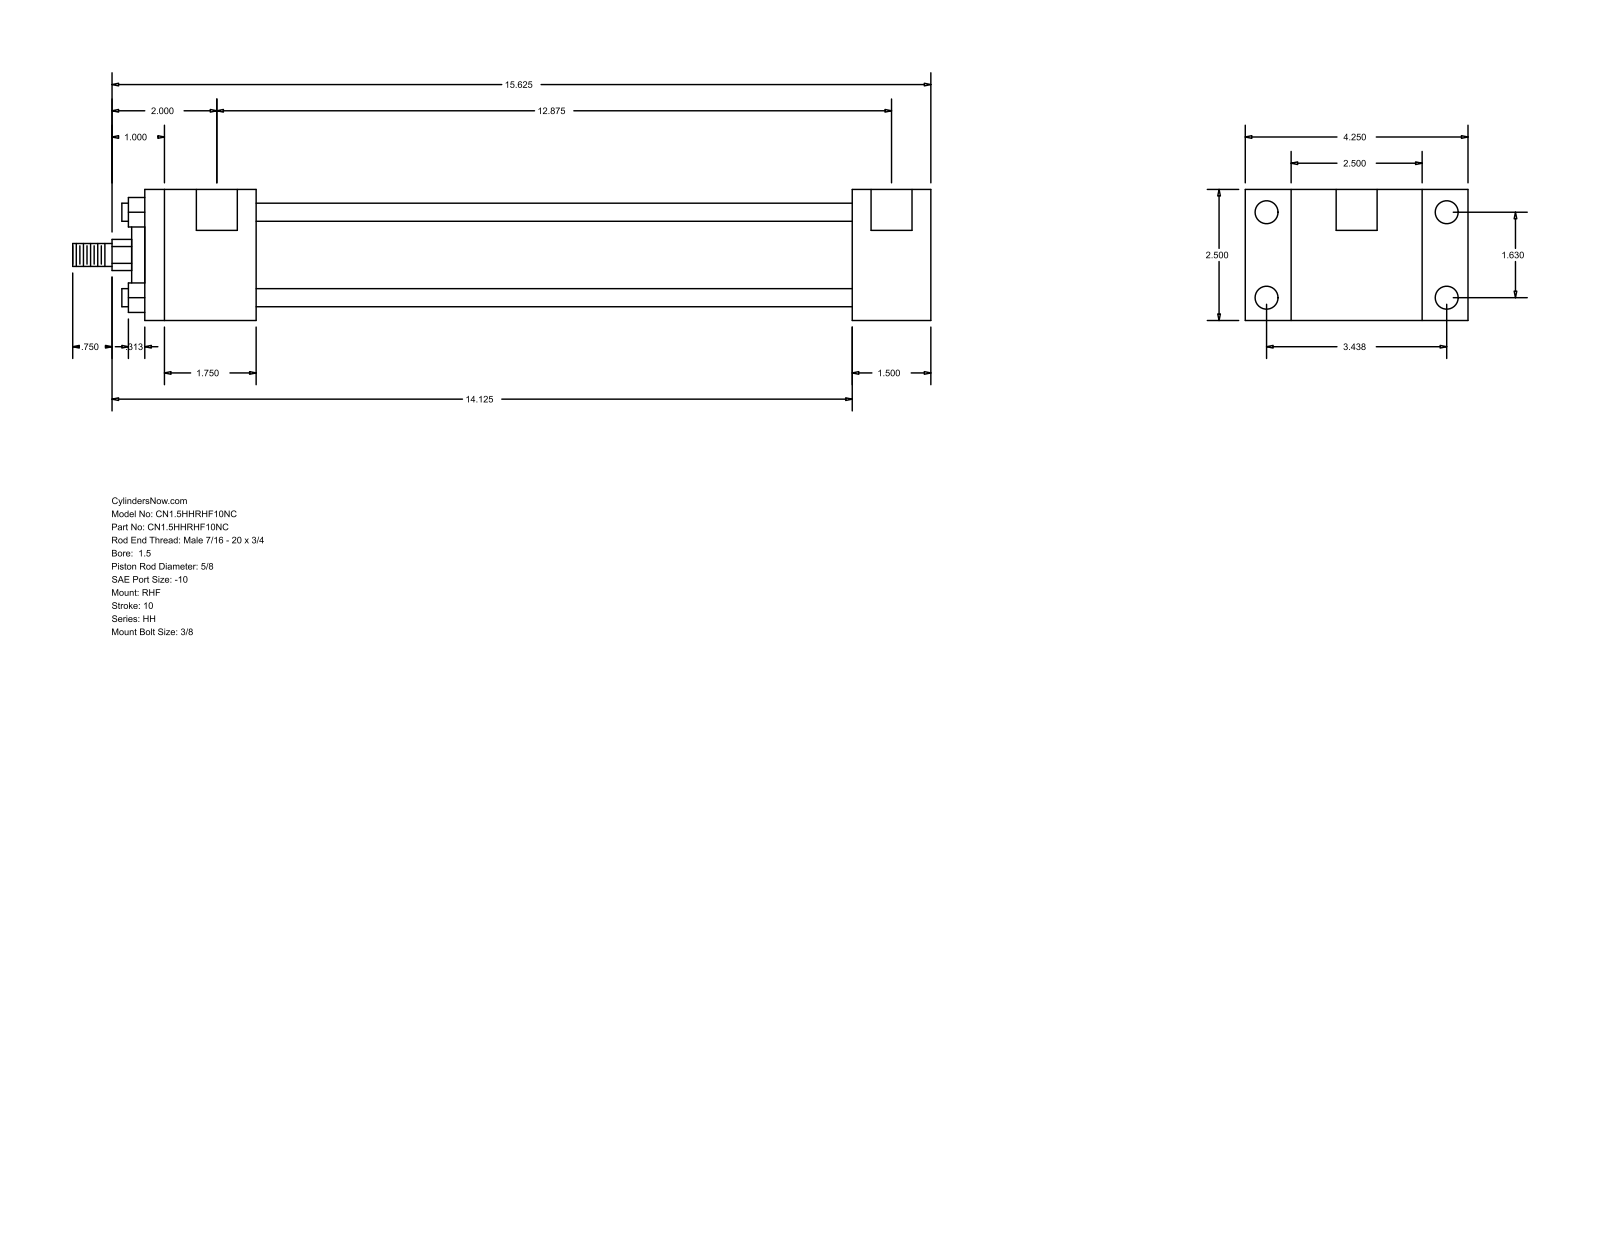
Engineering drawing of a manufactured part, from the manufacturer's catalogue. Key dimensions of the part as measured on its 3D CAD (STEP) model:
Part name (STEP PRODUCT): HH_RHF__0150_0.625
STEP written by: GSSL Pune (CONFIG_CONTROL_DESIGN)
Units: millimetres
Bodies: 0 solids, 88 faces (60 planar, 28 cylindrical, 0 other)
Overall size (bounding box): 415.93 × 107.95 × 63.5
Round holes (diameter × count): ⌀5.56 ×4, ⌀11.13 ×4, ⌀19.84 ×2
Round bosses / shafts (diameter × count): ⌀8.76 ×4, ⌀44.45 ×1, ⌀28.57 ×1, ⌀15.88 ×1, ⌀11.11 ×1
Partial cylindrical surfaces — rounded edges, fillets, slot ends (radius × count): R7.54 ×1
Main face-to-face distances: 63.5, 22.23, 85.73, 38.11, 342.89, 381, 107.96, 53.97, 288.92, 327.03
Hole centre spacings: 1.59, 41.4, 87.32, 96.64, 328.61, 330.2, 327.02
